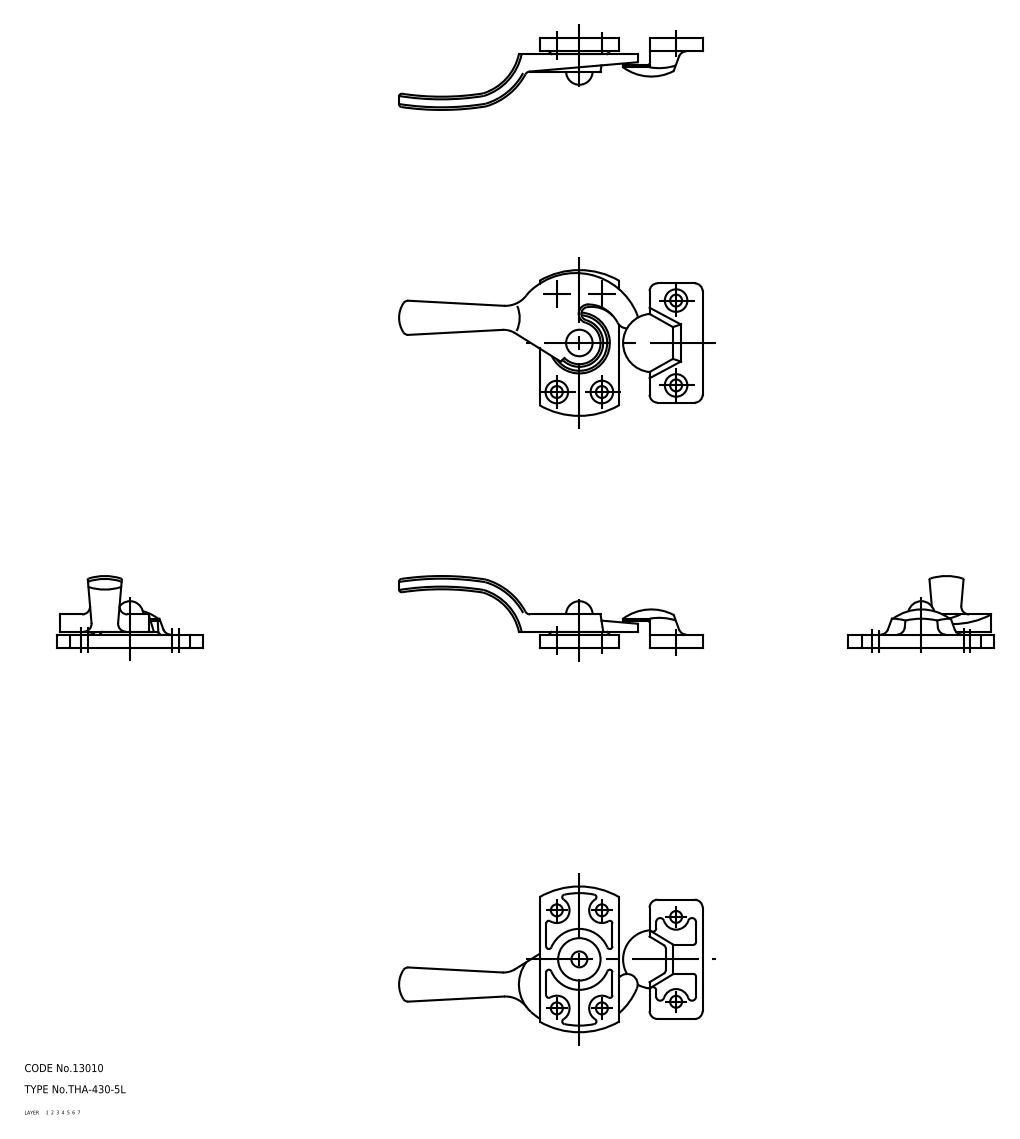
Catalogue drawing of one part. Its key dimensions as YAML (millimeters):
part_name: "washer_C; washer_B; rivet; keeper (+3 more)"
step_written_by: "CADfix (AUTOMOTIVE_DESIGN)"
units: millimeters
bodies: {solids: 6, faces: 166, planar: 0, cylindrical: 0, other: 166}
overall_size: [114.5, 55, 27.1]
volume: 18875
surface_area: 12963
